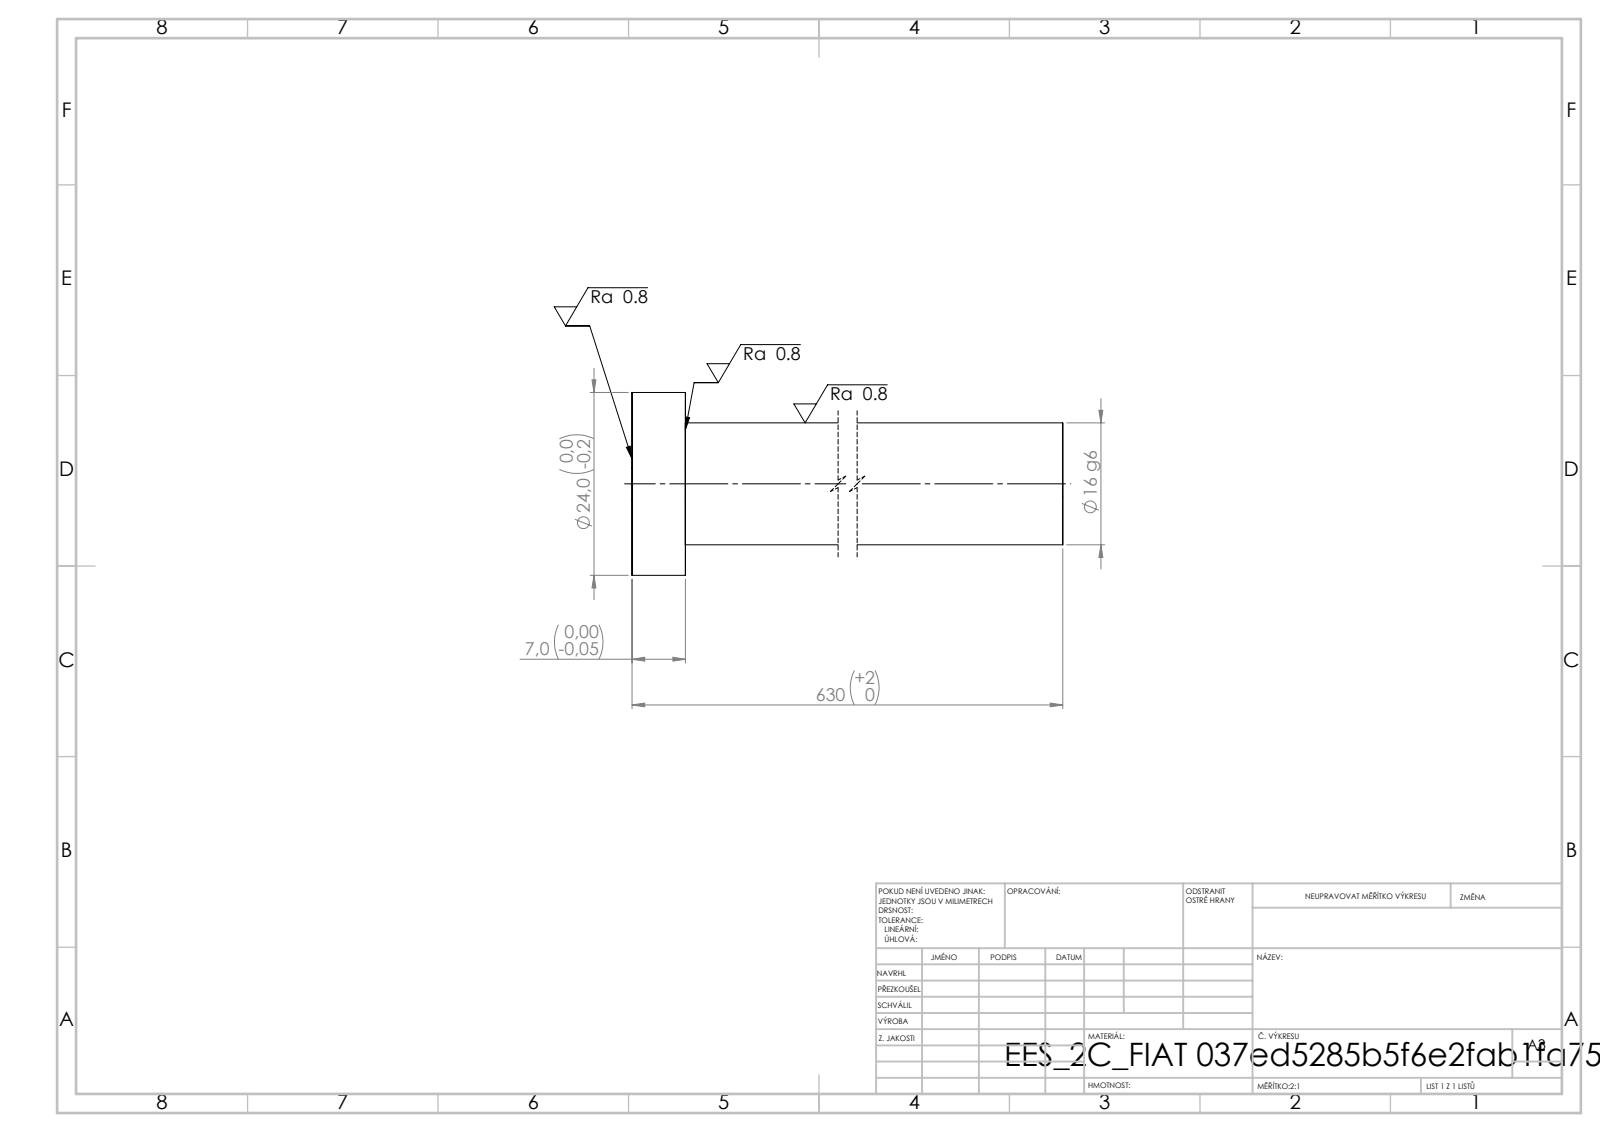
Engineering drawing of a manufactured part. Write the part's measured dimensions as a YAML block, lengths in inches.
step_written_by: "SolidWorks 2019 (CONFIG_CONTROL_DESIGN)"
units: inches
bodies: {solids: 1, faces: 7, planar: 3, cylindrical: 4, other: 0}
overall_size: [24.803, 0.945, 0.945]
volume: 7.837
surface_area: 50.76
round_bosses_or_shafts:
  - {diameter: 0.945, count: 1}
  - {diameter: 0.63, count: 1}
face_to_face_distances: [0.276, 24.803, 24.528]
